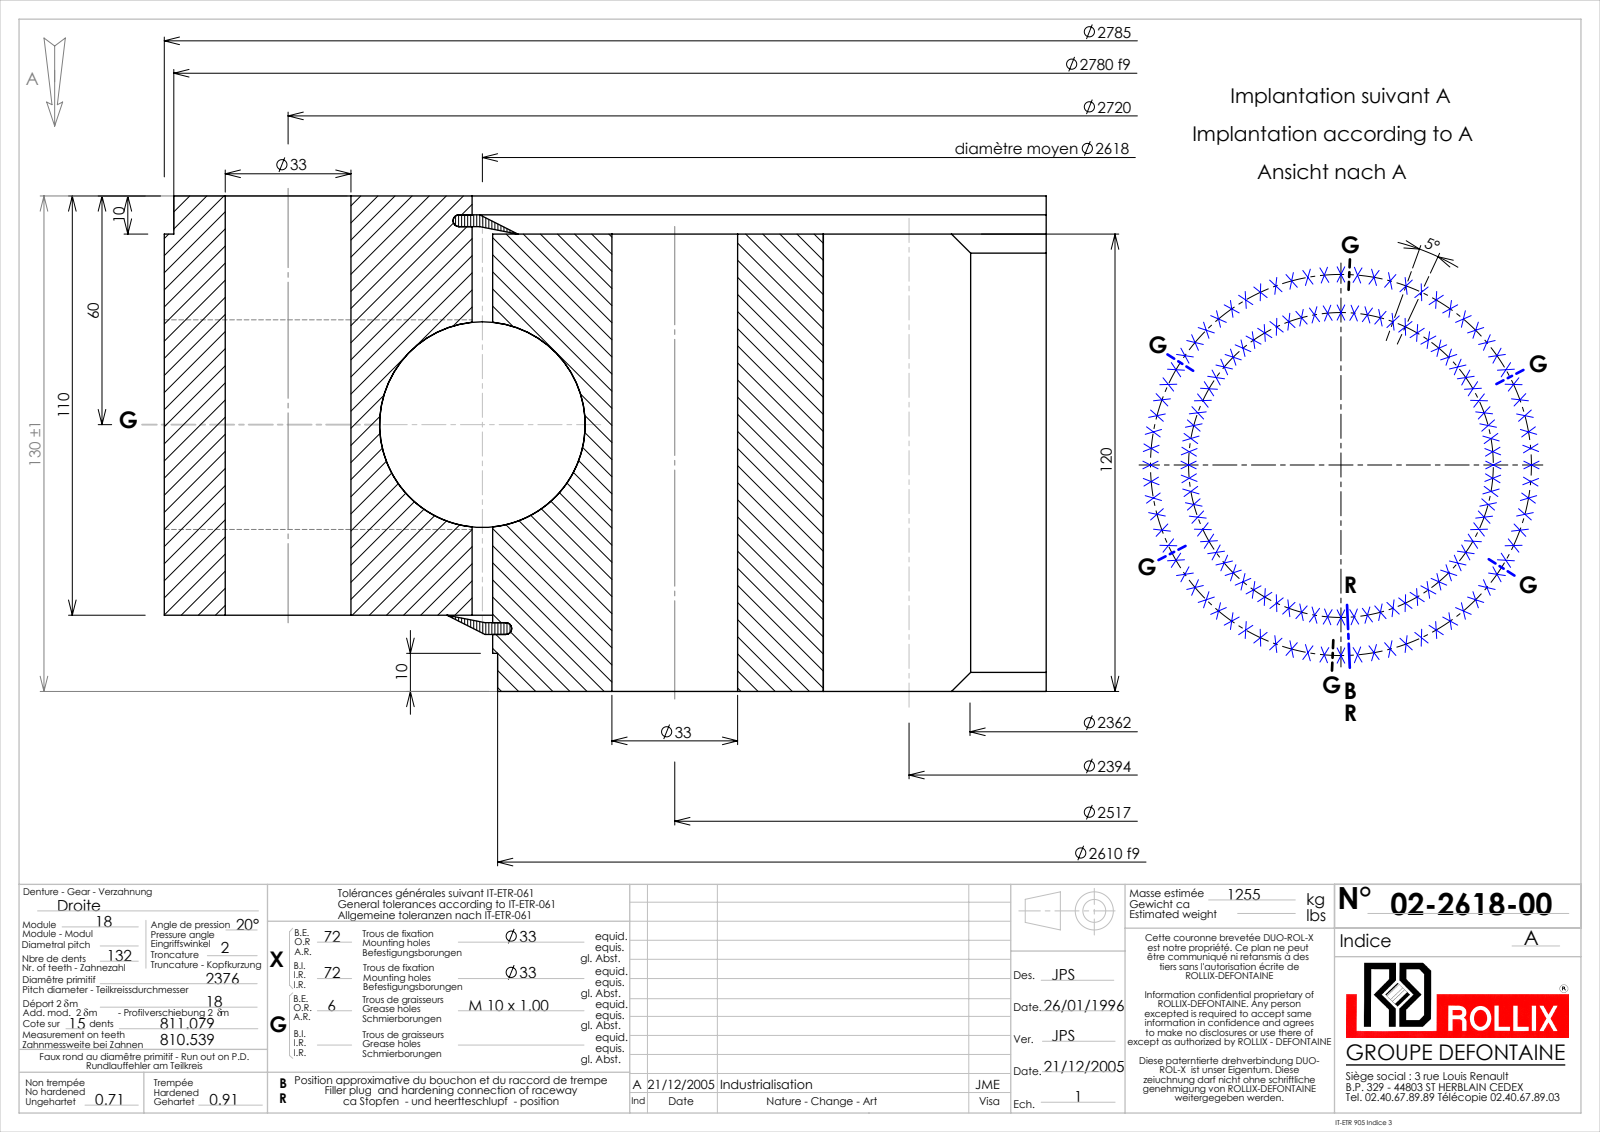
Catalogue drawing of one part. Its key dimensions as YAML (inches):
part_name: "02-2618-00"
step_written_by: "SolidWorks 2016 (CONFIG_CONTROL_DESIGN)"
units: inches
bodies: {solids: 5, faces: 1165, planar: 278, cylindrical: 583, other: 304}
overall_size: [109.646, 109.646, 5.118]
volume: 8940
surface_area: 15980
round_holes:
  - {diameter: 1.299, count: 144}
  - {diameter: 0.354, count: 6}
  - {diameter: 103.283, count: 1}
round_bosses_or_shafts:
  - {diameter: 109.646, count: 1}
  - {diameter: 109.449, count: 1}
  - {diameter: 102.858, count: 1}
  - {diameter: 102.756, count: 1}
partial_cylinders:
  - {radius: 46.496, count: 1}
  - {radius: 48.012, count: 1}
face_to_face_distances: [4.724, 0.787, 3.937, 0.394, 4.331, 5.118, 0.199, 4.136, 0.122, 0.077]
hole_center_spacings: [4.322, 8.637, 17.207, 12.934, 21.448, 56.838, 29.798, 33.892]
